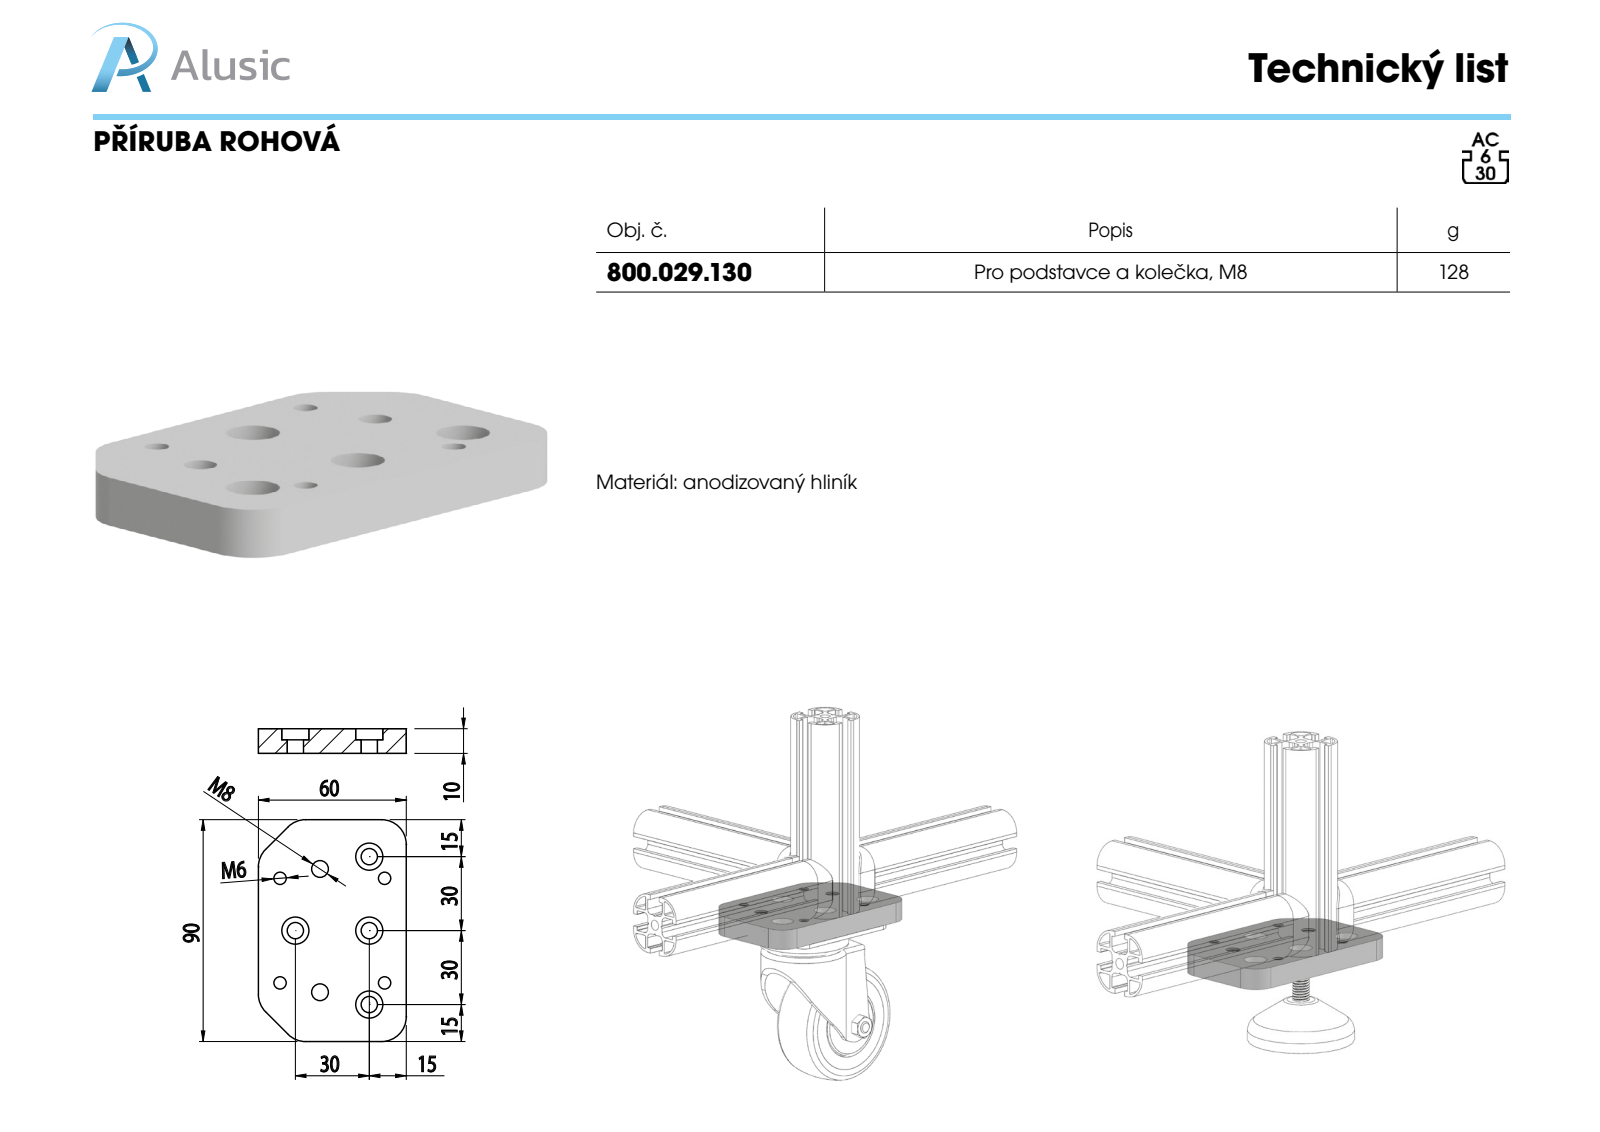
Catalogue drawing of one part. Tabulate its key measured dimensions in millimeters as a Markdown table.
| quantity | value |
| --- | --- |
| part name | 800.029.130 |
| STEP written by | SolidWorks 2012 (AUTOMOTIVE_DESIGN) |
| units | millimeters |
| bodies | 1 solid, 32 faces (12 planar, 20 cylindrical, 0 other) |
| overall size | 90 × 60 × 10 |
| volume | 47 260 mm³ |
| surface area | 14 526 mm² |
| round holes (diameter × count) | 5 × 4, 6.6 × 4, 11 × 4, 6.8 × 2 |
| partial cylindrical surfaces (radius × count) | 10 × 6 |
| main face-to-face distances | 10, 60, 90, 5.5, 4.5 |
| hole center spacings | 22.1, 41.96, 42.42, 30, 10.76, 16.65, 20.62, 26.48 |
